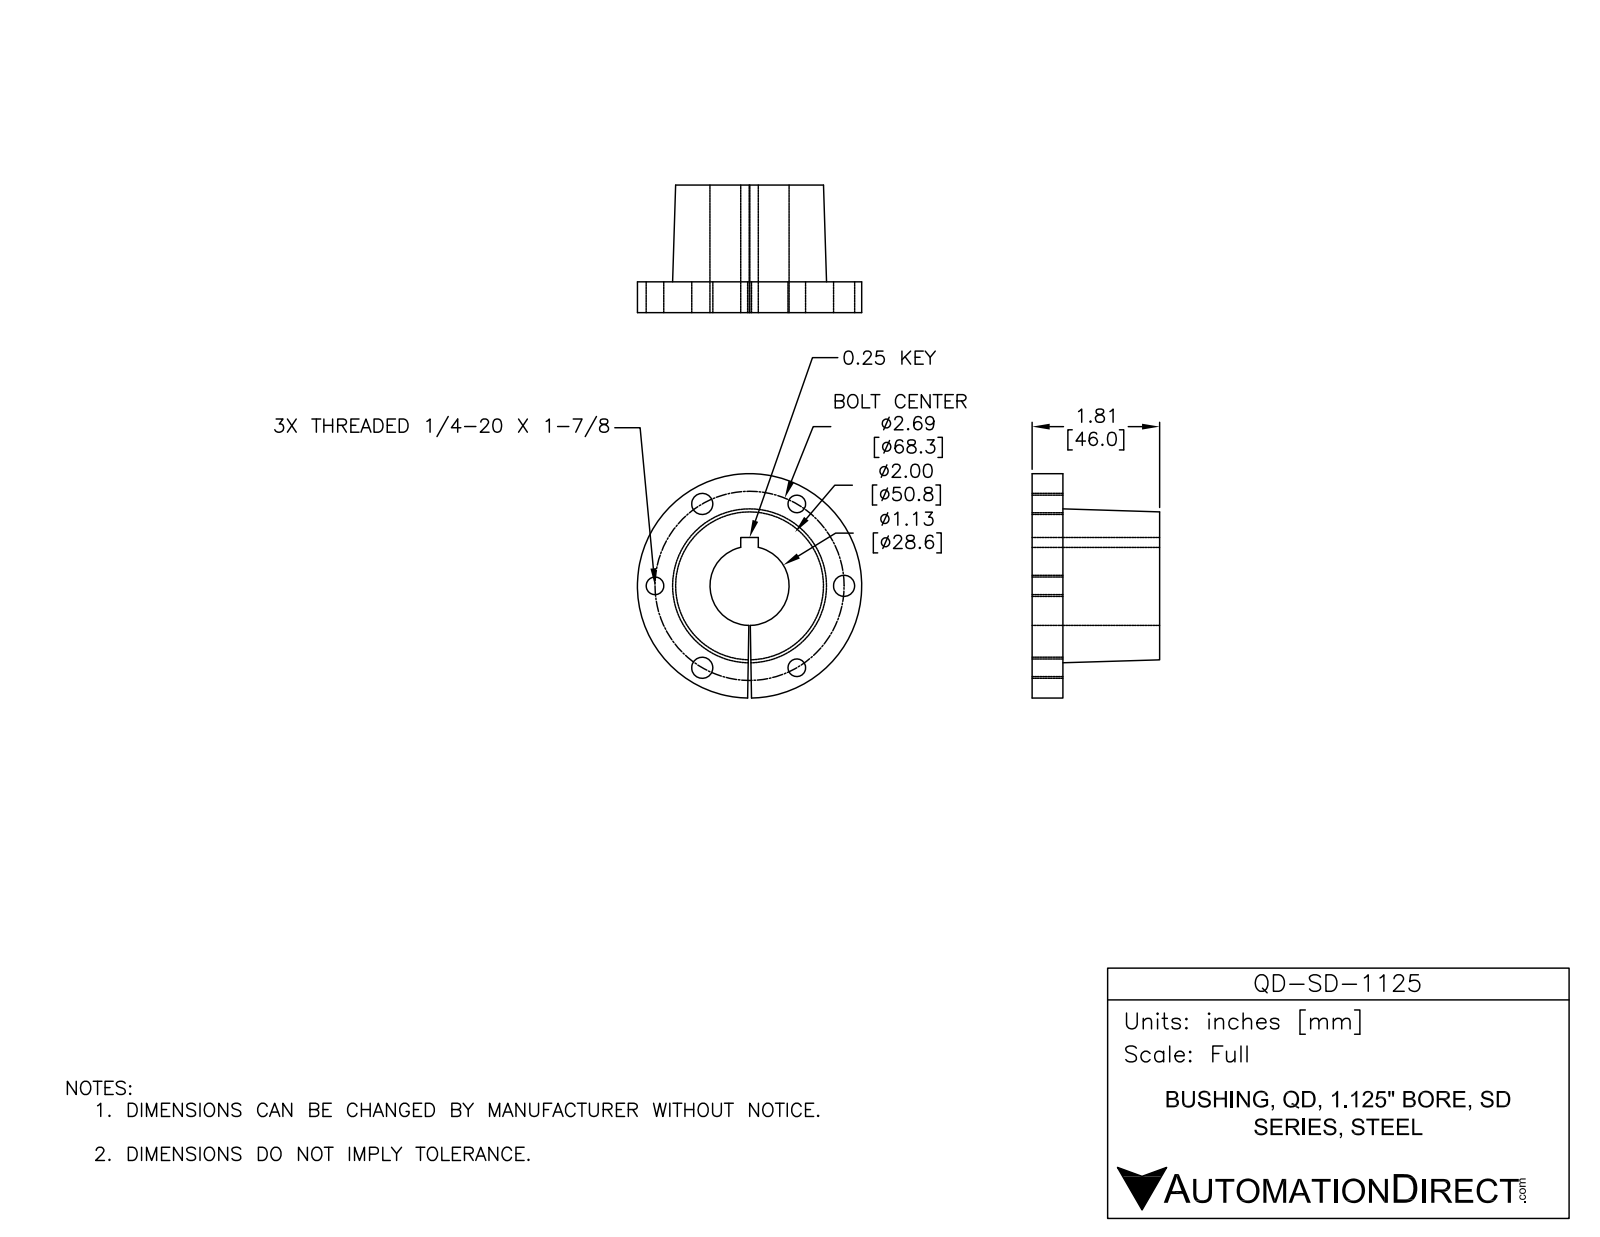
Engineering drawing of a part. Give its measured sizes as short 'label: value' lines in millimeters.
name: QD-SD-1125
written by: SolidWorks 2014 (AUTOMOTIVE_DESIGN)
unit: mm
bodies: 1 solid, 29 faces (8 planar, 18 cylindrical, 3 other)
size: 81 × 80.9 × 46.1
volume: 105 100 mm³; area: 24 380 mm²
holes: 3× ⌀6.4, 3× ⌀7.6, 1× ⌀28.6
bosses: 1× ⌀80.9
face distances: 11.1, 46, 34.9, 6.4
hole spacings: 34.1, 59.1, 34.1, 68.3, 68.2
